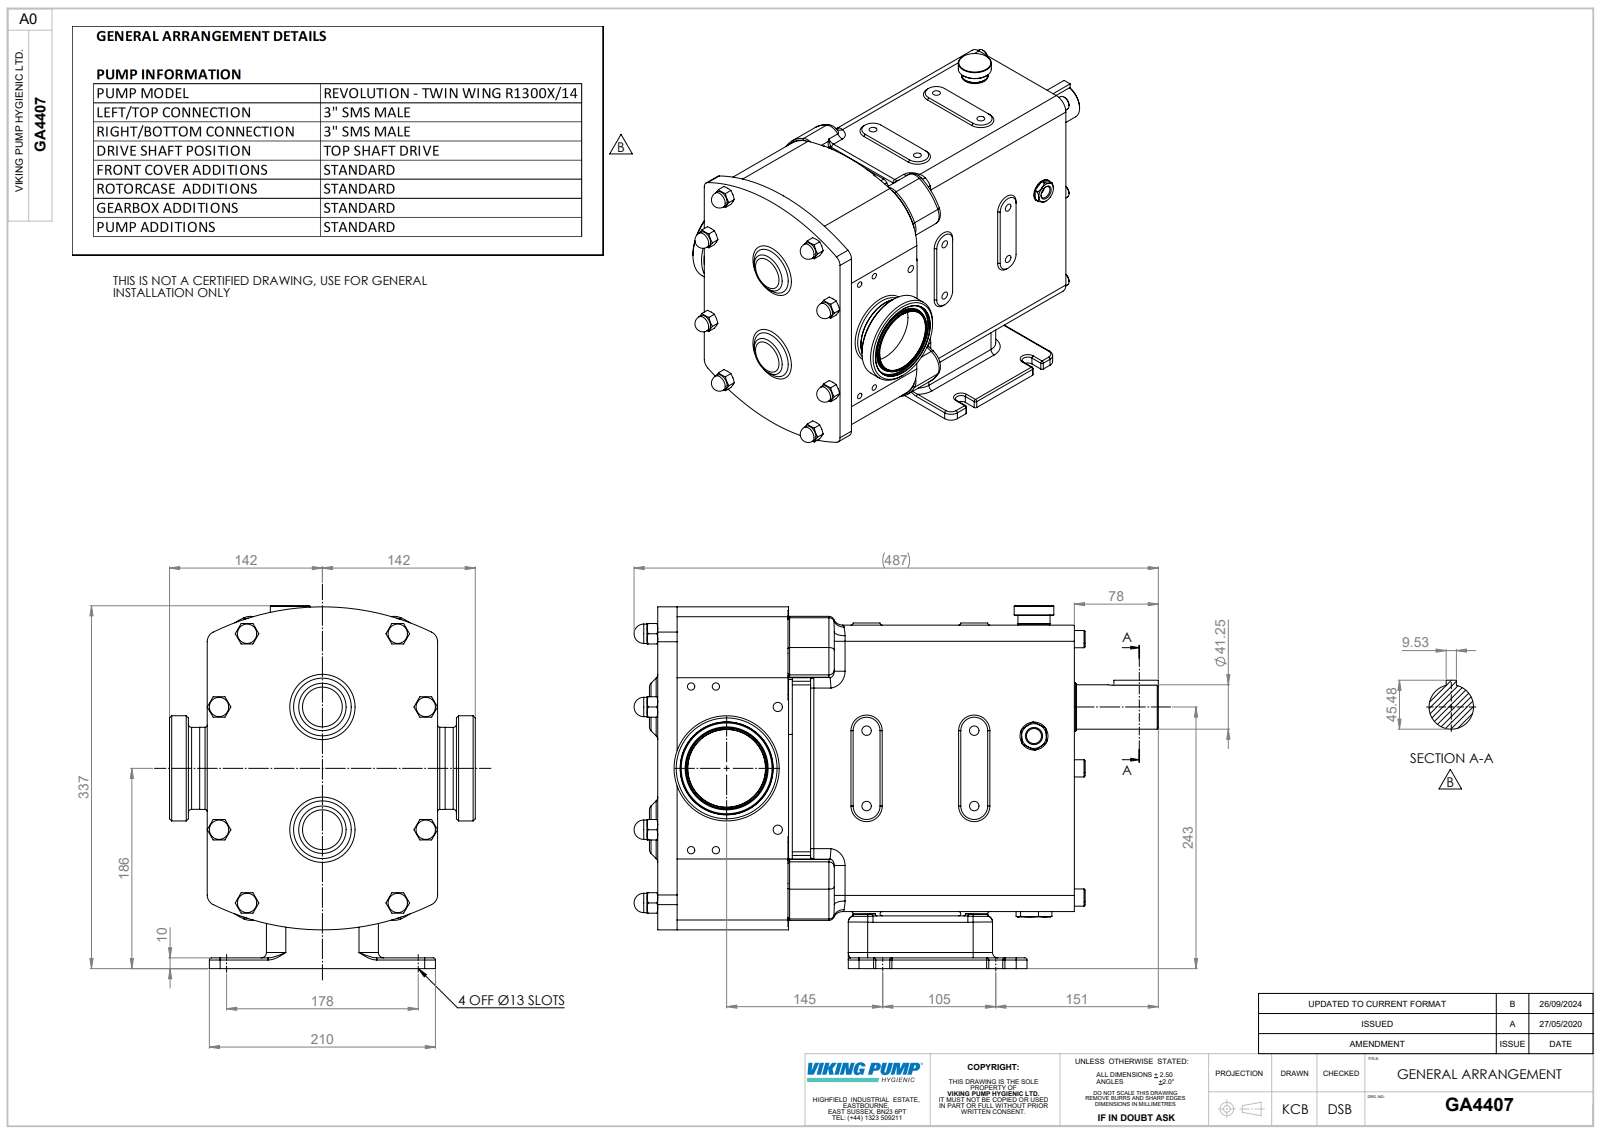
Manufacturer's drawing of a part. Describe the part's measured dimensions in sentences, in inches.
The part is named "Copy of R1300 CPP H TSD^GA4407; GA4407; Copy of Z94-5101-55 - 3 INCH SMS681^GA4407". Its 3-D file was written by "SolidWorks 2023 (AUTOMOTIVE_DESIGN)". It is 3 solids with 968 faces: 303 planar, 292 cylindrical and 373 other. Overall it measures 19.173 by 13.268 by 11.181 inches. Its volume is 1 144 cubic inches and its surface area 1 123 square inches. Round holes: 8 of diameter 0.346, 4 of diameter 0.268, 2 of diameter 0.339, 1 of diameter 0.551, 1 of diameter 1.331, 1 of diameter 2.843, 1 of diameter 3.386. Round bosses or shafts: 8 of diameter 0.709, 6 of diameter 0.63, 1 of diameter 3.846, 1 of diameter 3.004, 1 of diameter 2.996, 1 of diameter 2.972, 1 of diameter 2.008, 1 of diameter 1.772. Partial cylindrical surfaces (rounded edges, fillets, slot ends): 38 of radius 0.079, 30 of radius 0.394, 19 of radius 0.197, 8 of radius 0.232, 8 of radius 0.591, 8 of radius 0.709, 4 of radius 0.118, 4 of radius 0.236. The main face-to-face distances are 5.984, 4.783, 10.453, 15.236, 7.205, 1.22, 4.921, 0.138, 10.315, 1.693. The hole center spacings are 2.756, 3.937, 4.806, 0.906, 2.194, 2.384, 2.921, 3.018.
